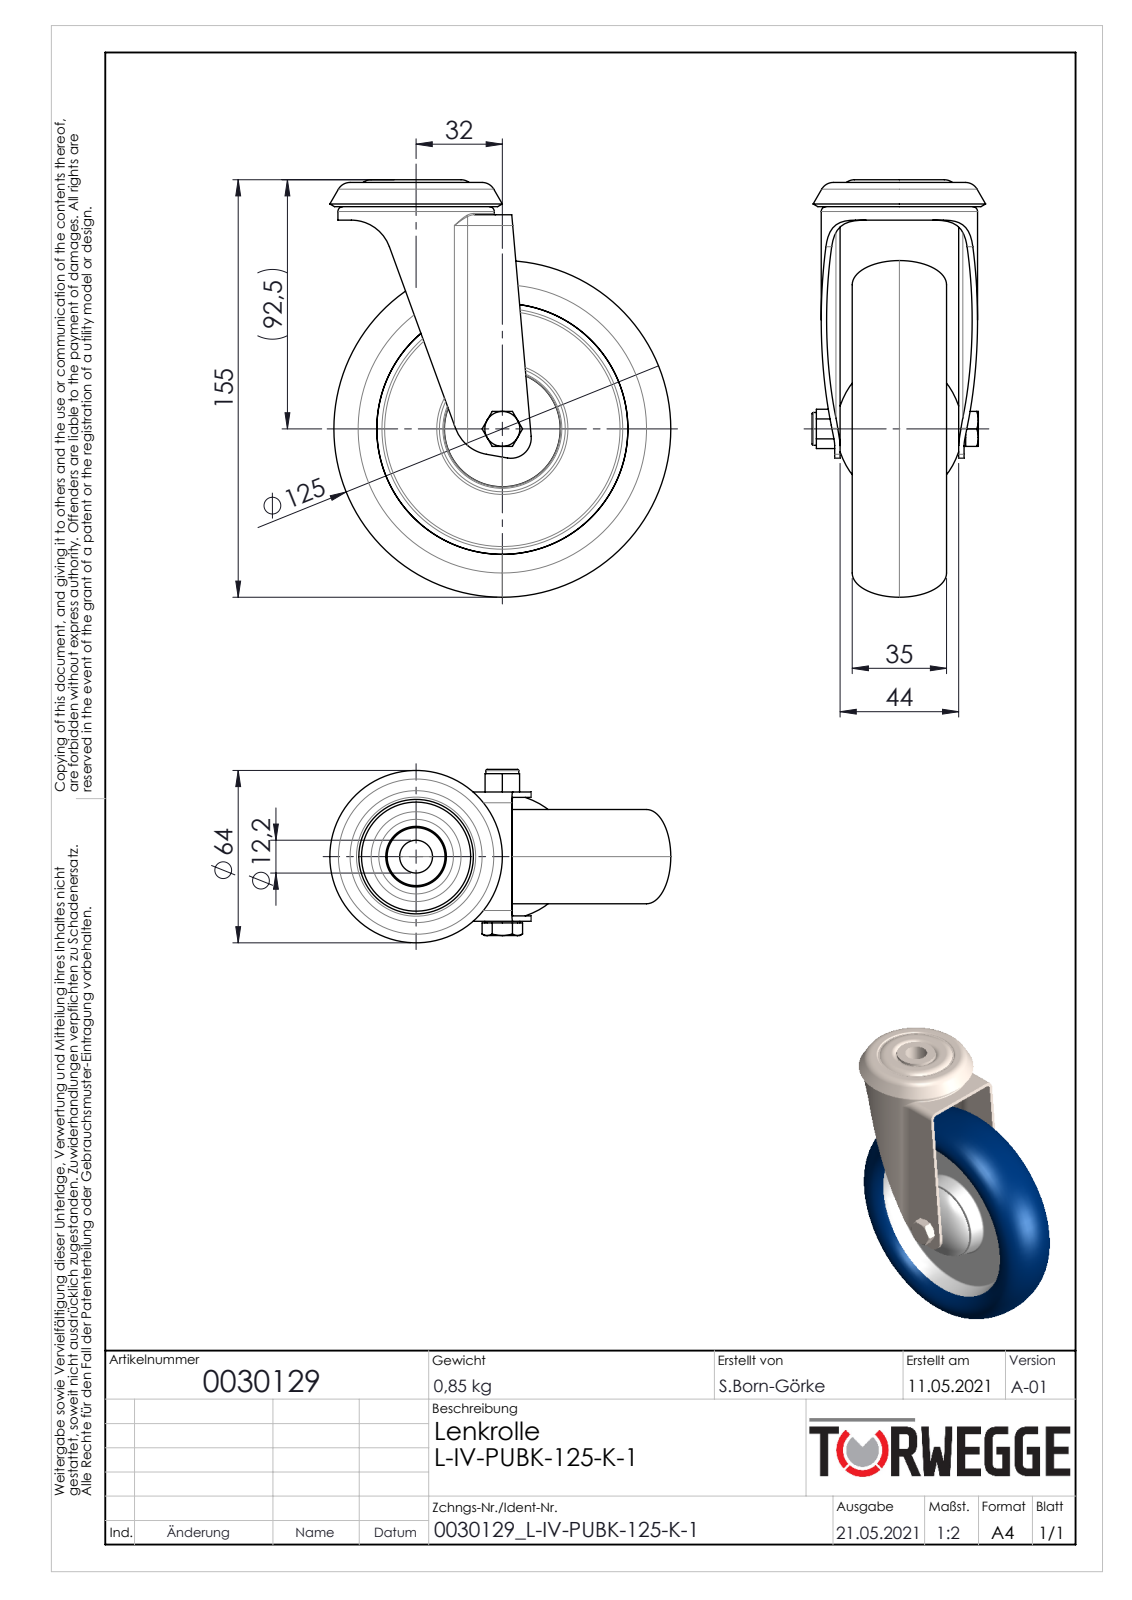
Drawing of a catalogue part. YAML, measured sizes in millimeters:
part_name: "0030129"
step_written_by: "SolidWorks 2020 (AUTOMOTIVE_DESIGN)"
units: millimeters
bodies: {solids: 7, faces: 215, planar: 59, cylindrical: 52, other: 104}
overall_size: [155, 126.5, 64.4]
volume: 280050
surface_area: 112545
round_holes:
  - {diameter: 6.65, count: 1}
  - {diameter: 8, count: 1}
  - {diameter: 8.2, count: 1}
  - {diameter: 12.2, count: 1}
  - {diameter: 33, count: 1}
  - {diameter: 35, count: 1}
  - {diameter: 54, count: 1}
round_bosses_or_shafts:
  - {diameter: 58, count: 1}
  - {diameter: 29, count: 1}
  - {diameter: 21.5, count: 1}
  - {diameter: 15, count: 1}
  - {diameter: 13, count: 1}
  - {diameter: 12.2, count: 1}
partial_cylinders:
  - {radius: 2, count: 2}
  - {radius: 4, count: 2}
  - {radius: 10, count: 2}
  - {radius: 12, count: 2}
  - {radius: 15, count: 2}
  - {radius: 7.5, count: 1}
face_to_face_distances: [5, 2, 21.5, 19.5, 24.5, 26.5, 46, 13.25, 9.25, 12.25]
